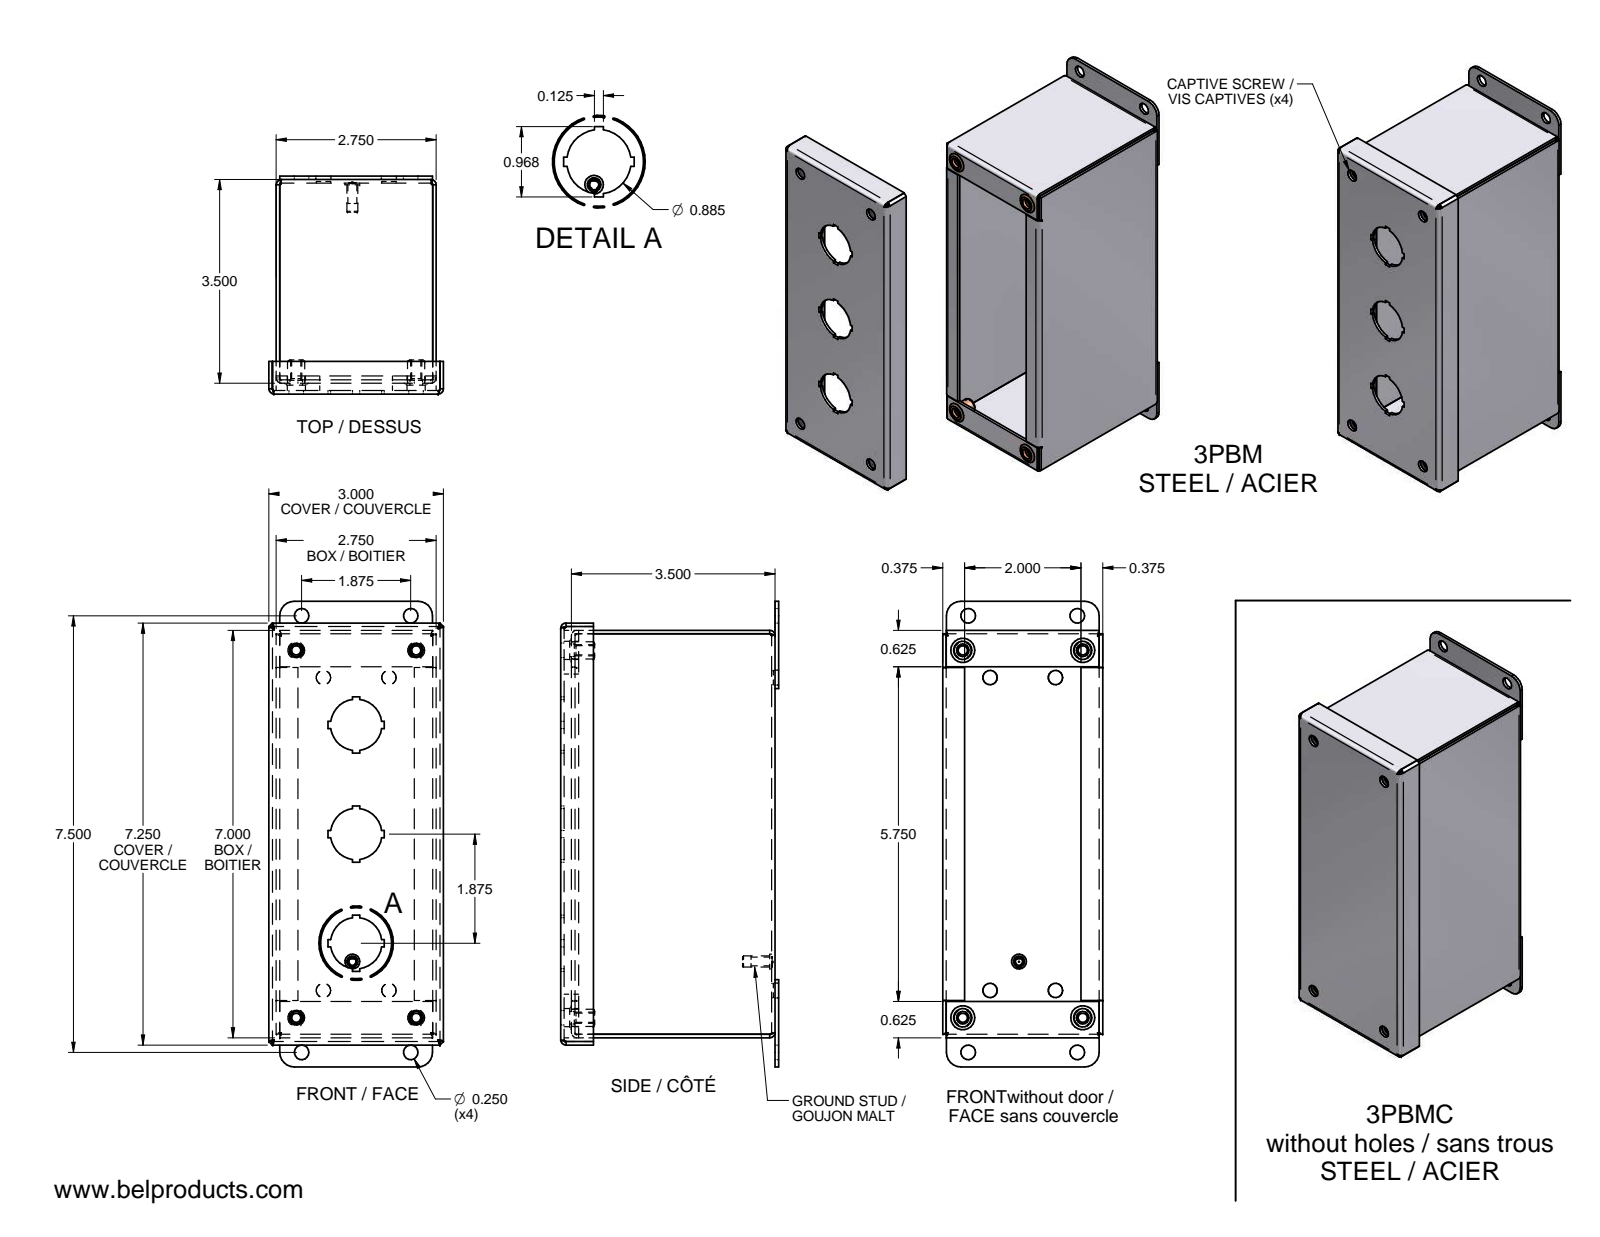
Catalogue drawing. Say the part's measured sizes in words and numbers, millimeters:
The part is named "3PBM_BOITIER; 3PBM-B; INSERT 10-32 AVK ALS4-1032-130; 3PBM-P (+4 more)". Its 3-D file was written by "Unknown (AUTOMOTIVE_DESIGN)". It is 10 solids with 383 faces: 241 planar, 85 cylindrical and 57 other. Overall it measures 203.2 by 95.12 by 76.2 millimeters. Its volume is 175 506 cubic millimeters and its surface area 191 739 square millimeters. Round holes: 8 of diameter 6.35, 4 of diameter 4.04, 4 of diameter 5.49, 4 of diameter 6.22, 4 of diameter 6.73, 4 of diameter 7.37, 4 of diameter 7.92, 3 of diameter 22.48, 1 of diameter 3.17. Round bosses or shafts: 4 of diameter 7.52, 4 of diameter 6.35, 1 of diameter 6.5, 1 of diameter 4.83, 1 of diameter 3.02, 1 of diameter 0.51. Partial cylindrical surfaces (rounded edges, fillets, slot ends): 12 of radius 0.81, 12 of radius 2.34, 4 of radius 6.35. The main face-to-face distances are 1.52, 68.32, 92.08, 93.6, 69.84, 66.8, 3.18, 4.7, 176.28, 90.56. The hole center spacings are 15.28, 15.29, 16.79, 16.83, 25.1, 28.62, 41.74, 41.77.
